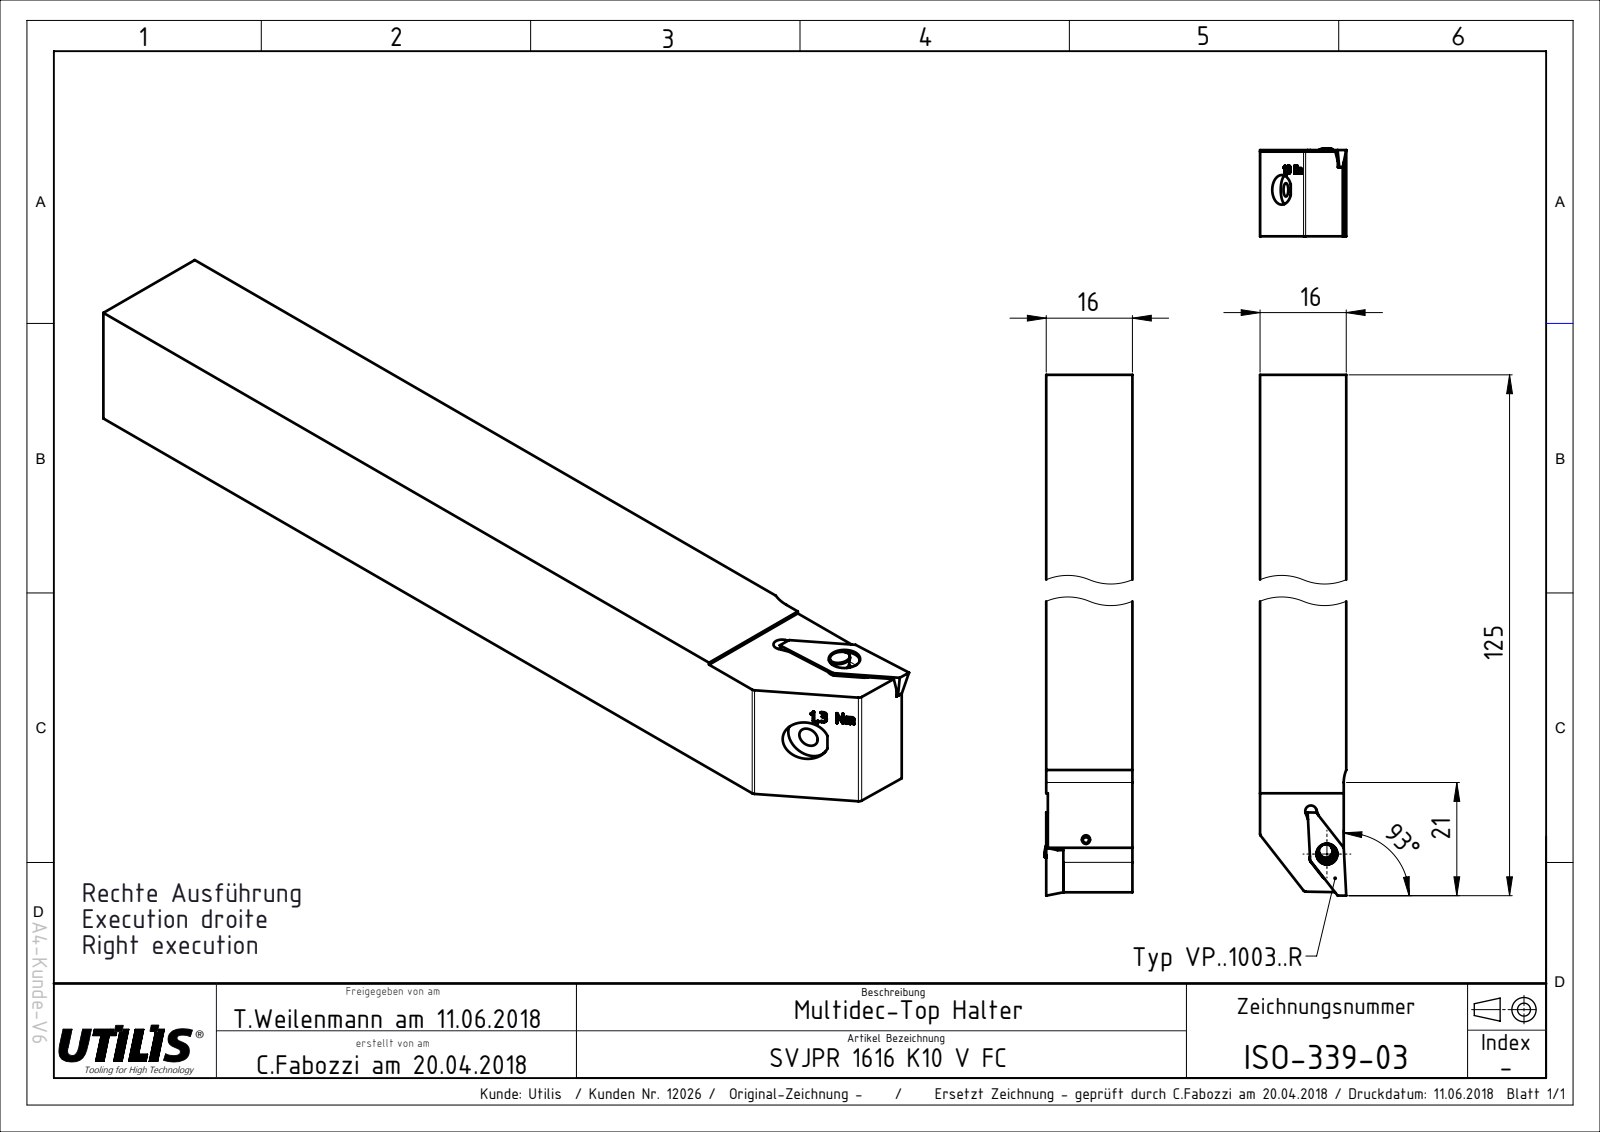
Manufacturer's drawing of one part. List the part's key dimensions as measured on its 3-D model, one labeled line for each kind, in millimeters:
Part name (STEP PRODUCT): ISO-339-03
STEP written by: SolidWorks 2018 (AUTOMOTIVE_DESIGN)
Units: millimetres
Bodies: 1 solid, 110 faces (58 planar, 8 cylindrical, 44 other)
Overall size (bounding box): 125 × 16 × 16
Volume: 30 850 mm³ · Surface area: 8 382 mm²
Partial cylindrical surfaces — rounded edges, fillets, slot ends (radius × count): R1.05 ×3, R0.5 ×2, R6 ×1, R6.1 ×1
Main face-to-face distances: 16, 15.53, 0.47, 15.7, 3.18, 2.88, 12.82, 4.32, 10.36, 6.04
